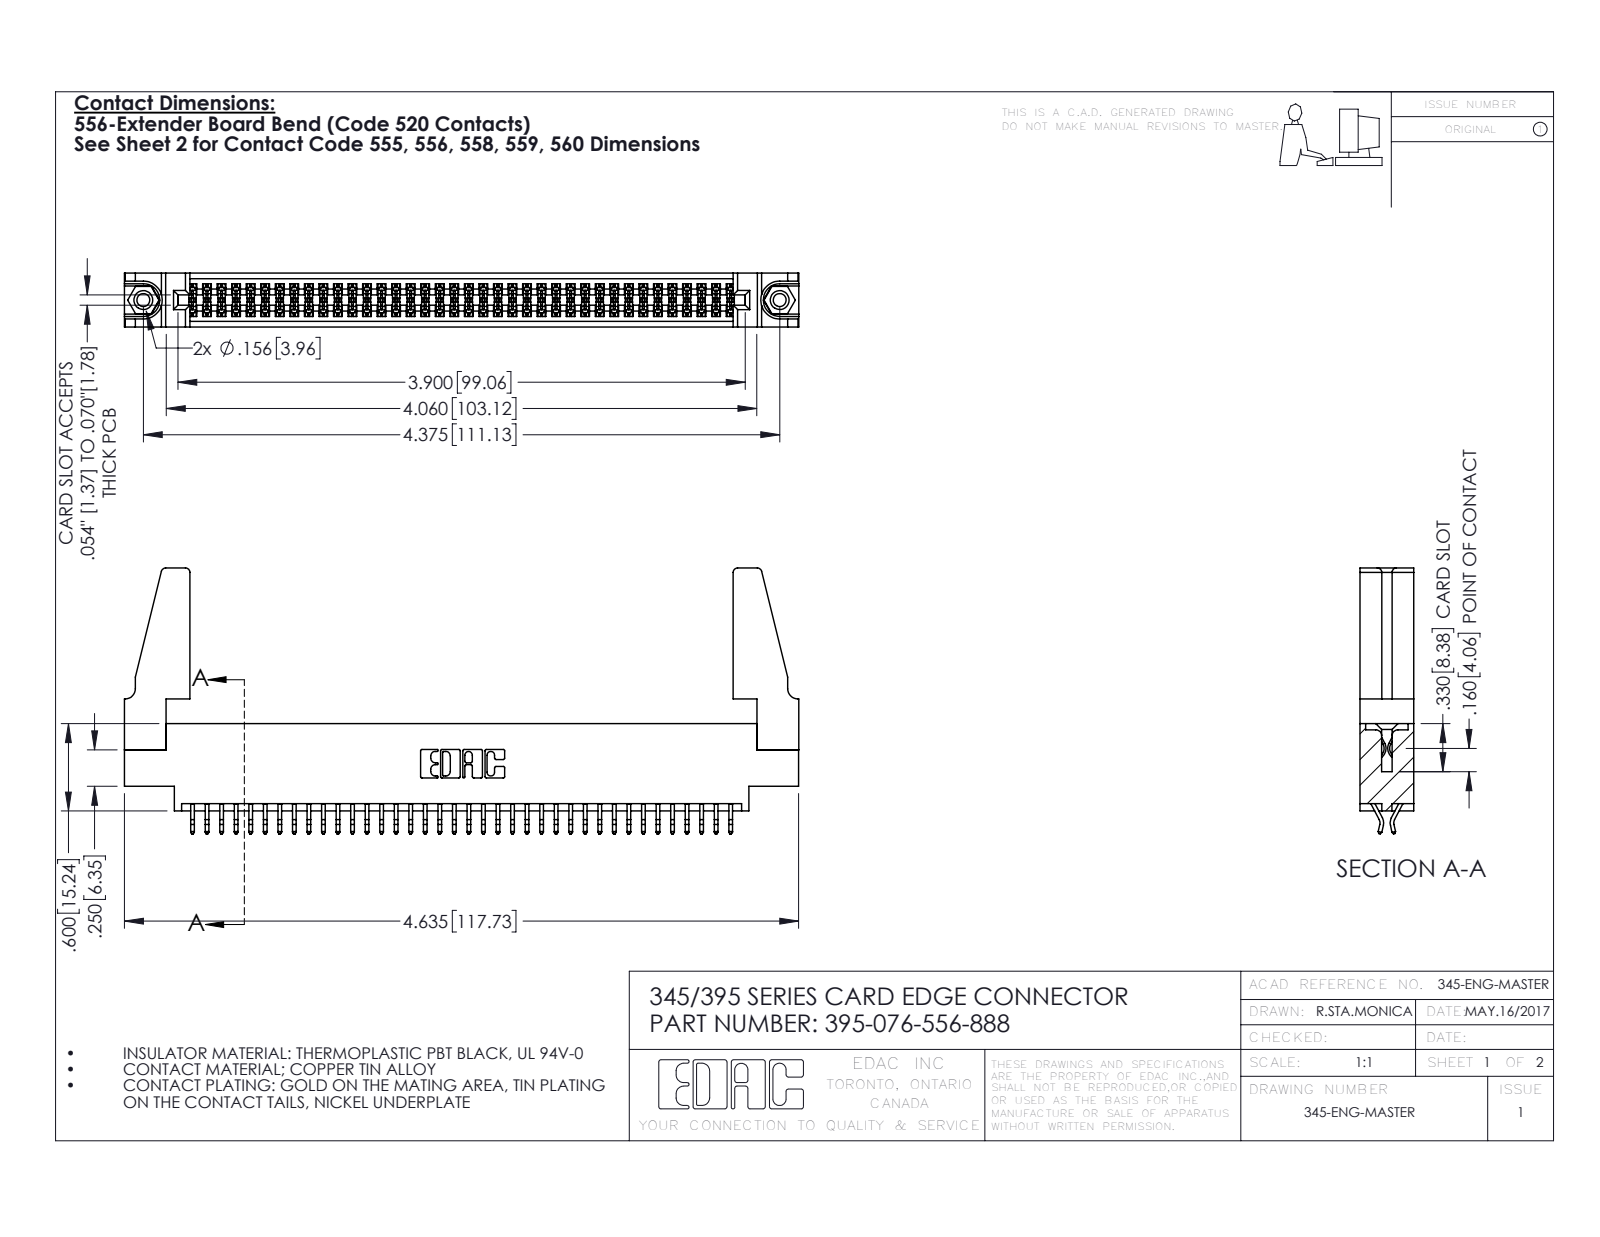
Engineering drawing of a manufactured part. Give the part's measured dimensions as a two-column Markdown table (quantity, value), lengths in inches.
| quantity | value |
| --- | --- |
| part name | 345 Part_0.170 Offset - 0.156 Dia-TH; 395-076-556-888; 345-292-001_556 Tail; 345-250-001_345-250-001-102 (+1 more) |
| STEP written by | SolidWorks 2016 (CONFIG_CONTROL_DESIGN) |
| units | inches |
| bodies | 81 solids, 4510 faces (2968 planar, 1526 cylindrical, 16 other) |
| overall size | 4.636 × 1.827 × 0.37 |
| volume | 0.887 in³ |
| surface area | 30.69 in² |
| round holes (diameter × count) | 0.089 × 2, 0.125 × 2, 0.156 × 2, 0.064 × 1 |
| round bosses / shafts (diameter × count) | 0.155 × 2 |
| partial cylindrical surfaces (radius × count) | 0.006 × 114, 0.01 × 22, 0.03 × 8, 0.007 × 6, 0.031 × 6, 0.026 × 3, 0.01 × 2, 0.014 × 2 |
| main face-to-face distances | 0.072, 0.298, 0.37, 0.025, 0.2, 0.098, 0.272, 0.225, 0.175, 0.149 |
| hole center spacings | 0.27, 4.139, 4.375 |
